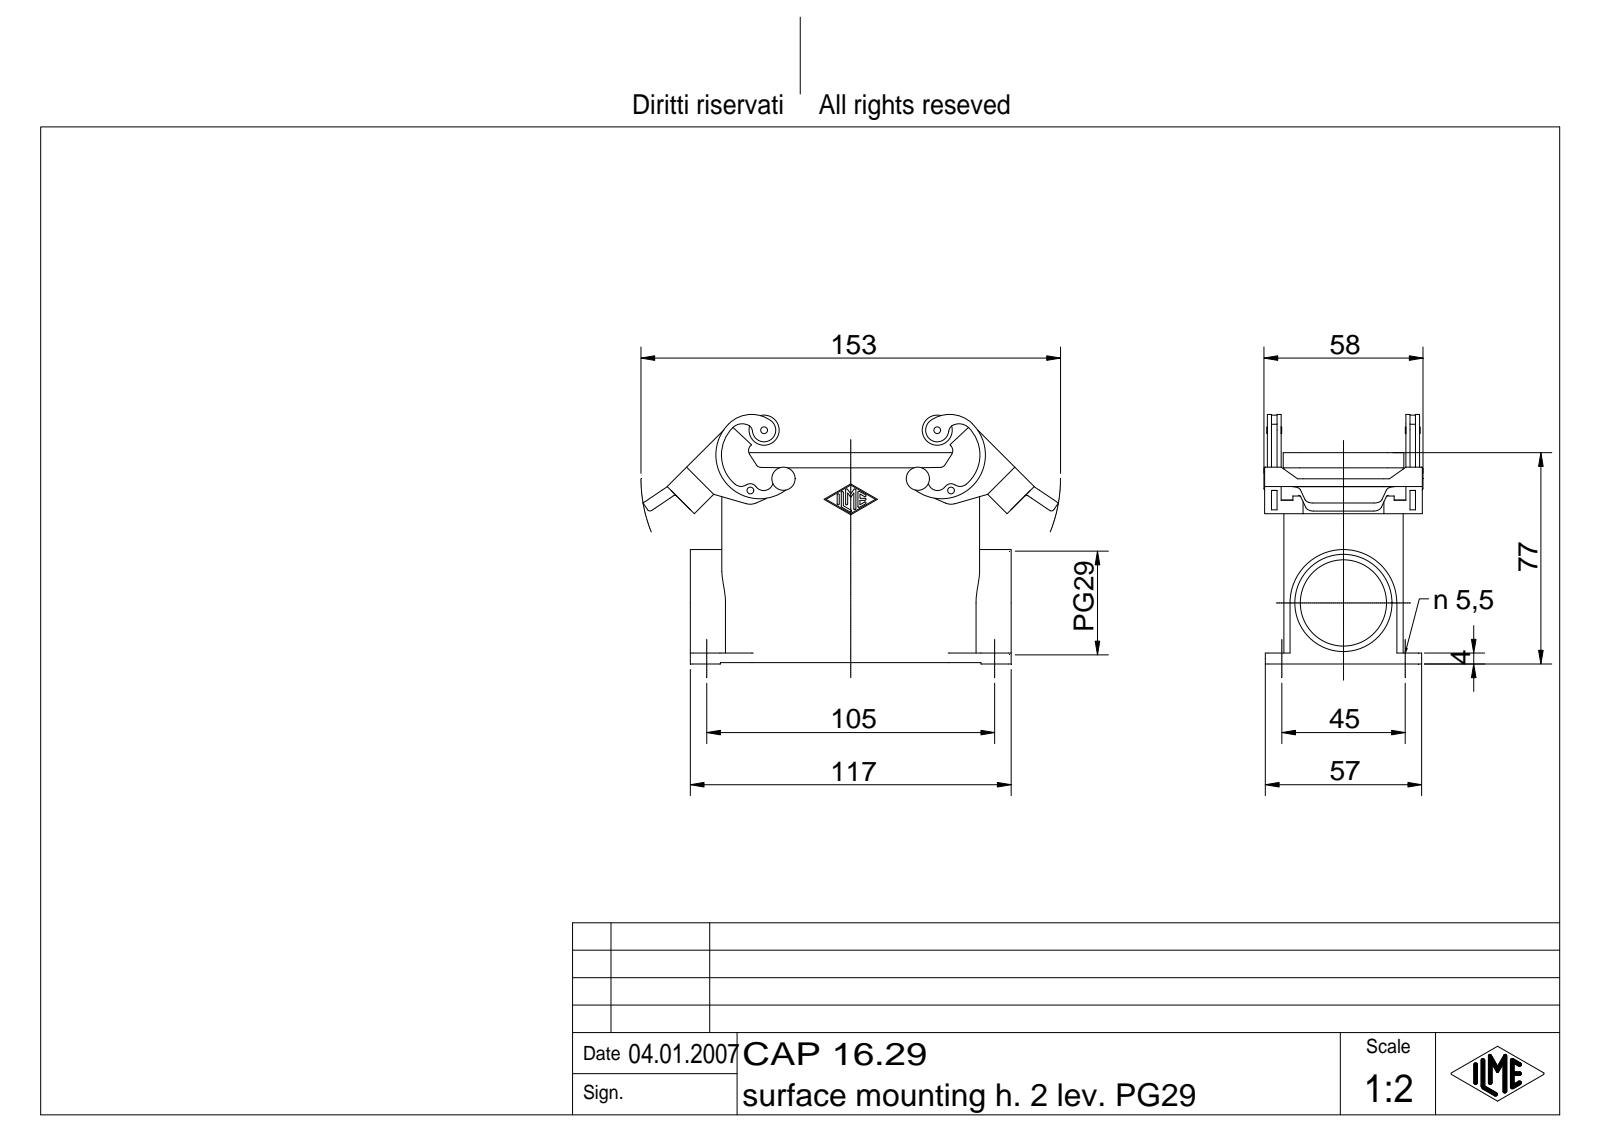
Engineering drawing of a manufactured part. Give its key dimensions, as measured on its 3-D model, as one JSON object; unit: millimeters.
{"part_name": "CAP 16.29", "step_written_by": "Autodesk Inventor 7 (AUTOMOTIVE_DESIGN)", "units": "millimeters", "bodies": {"solids": 1, "faces": 749, "planar": 191, "cylindrical": 205, "other": 353}, "overall_size": [151.49, 90.94, 58], "volume_mm3": 121604, "surface_area_mm2": 69720, "round_holes": [[2, 4], [5.5, 4], [2.5, 2], [31.48, 1], [35.48, 1]], "round_bosses_or_shafts": [[11, 2], [5, 2], [3, 2]], "partial_cylinders_radius": [[1, 20], [0.38, 14], [3, 12], [6, 8], [2.5, 6], [1.5, 4], [2, 4], [3.5, 4]], "face_to_face_distances": [3, 40.5, 43.5, 37.5, 3.5, 4, 0.75, 50.5, 40.75, 4.5], "hole_center_spacings": [22.56, 45, 71.62, 105, 114.24, 63.14, 73.18]}
